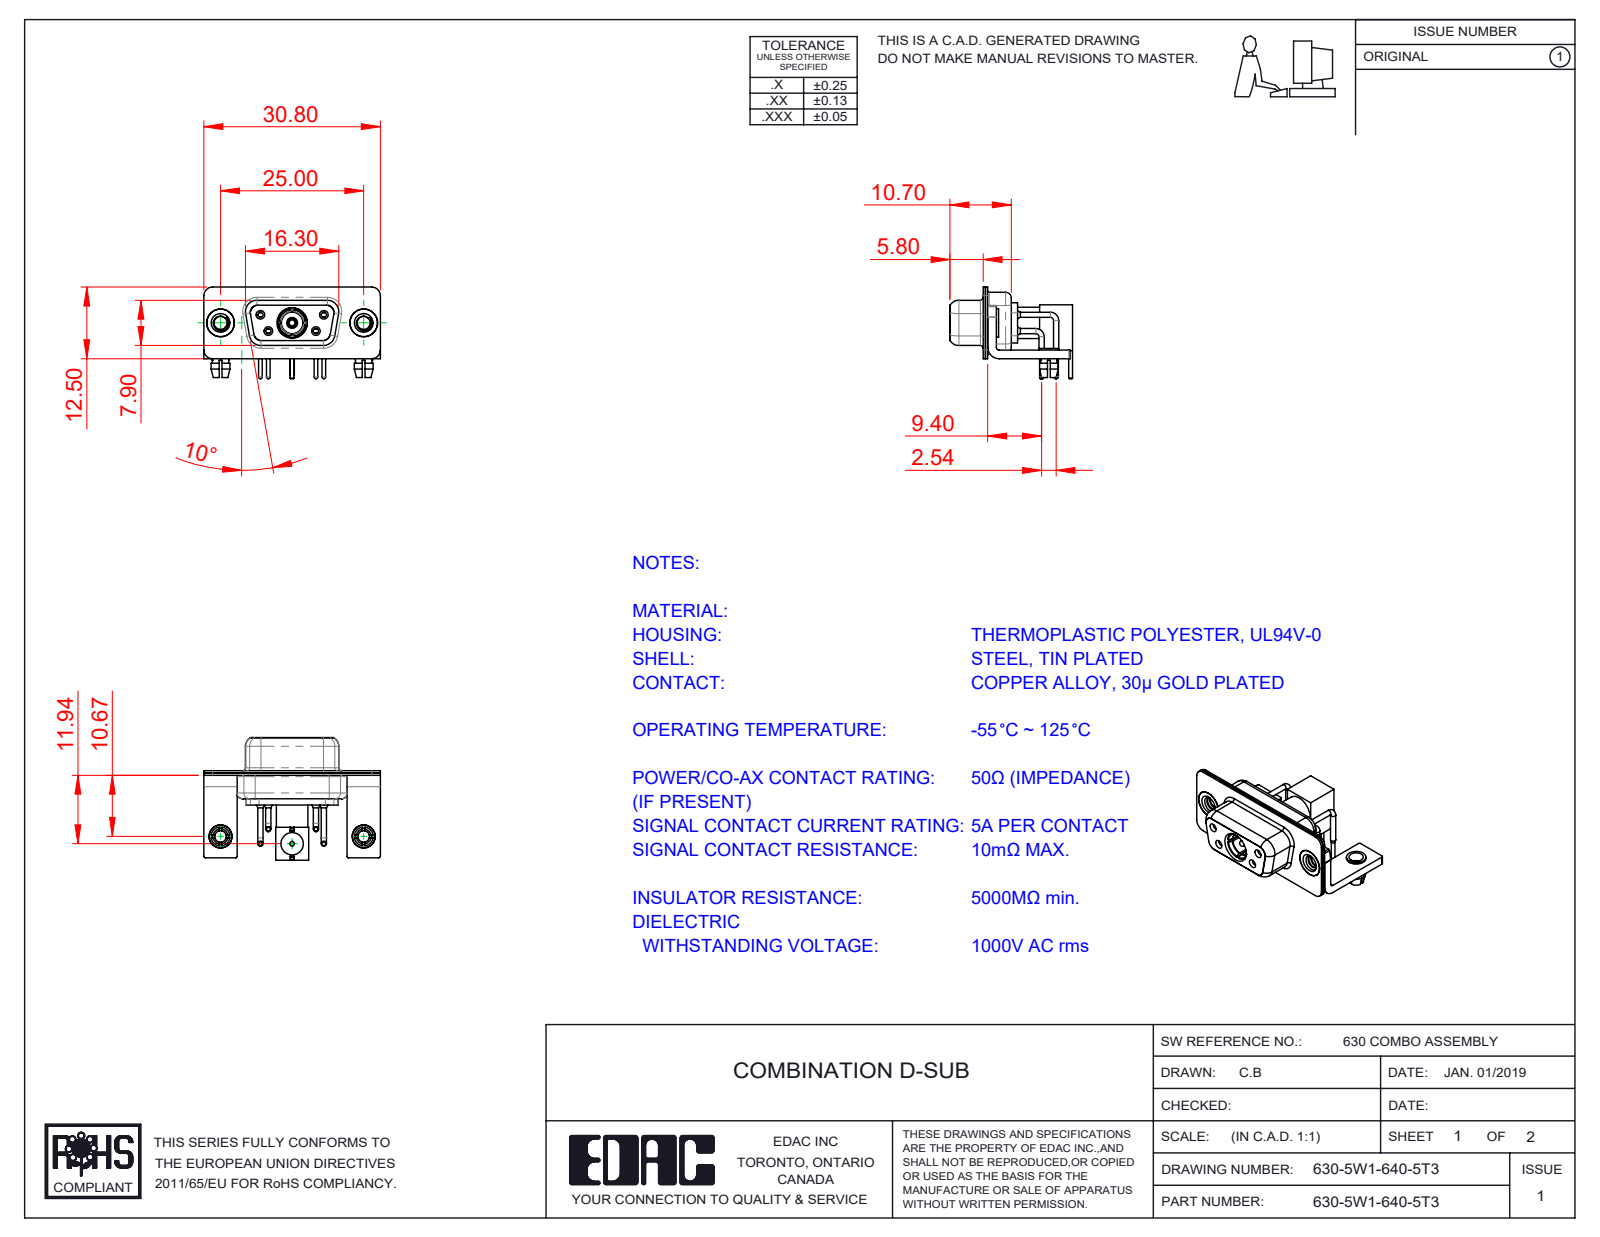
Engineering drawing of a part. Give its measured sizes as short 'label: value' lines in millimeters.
name: RA Back Shell; Pin_RA; Co-Ax Plug_RA PC Tail; 630Combo Housing_5W1 (+8 more)
written by: SolidWorks 2020 (CONFIG_CONTROL_DESIGN)
unit: mm
bodies: 19 solids, 791 faces (262 planar, 344 cylindrical, 185 other)
size: 30.8 × 21.41 × 16
volume: 2 275 mm³; area: 5 809 mm²
holes: 6× ⌀2, 5× ⌀1.1, 5× ⌀1.5, 4× ⌀0.9, 3× ⌀4.85, 2× ⌀1.6, 2× ⌀1.7, 2× ⌀2.26, 2× ⌀2.5, 2× ⌀3.2, 2× ⌀4, 2× ⌀4.05
bosses: 4× ⌀0.9, 4× ⌀0.65, 3× ⌀5, 3× ⌀4, 3× ⌀2.9, 2× ⌀4.95, 2× ⌀4.8, 2× ⌀3.4
rounds: 16× R0.25, 16× R1.5, 13× R2, 8× R1.35, 8× R1.6, 5× R0.5, 4× R0.6, 4× R0.65
face distances: 0.4, 0.8, 1.5, 1.4, 1.8, 0.45, 8.45, 2.3, 8.9, 8.5
hole spacings: 3.16, 5.72, 7.1, 12.5, 12.56, 18.1, 25, 4.39
